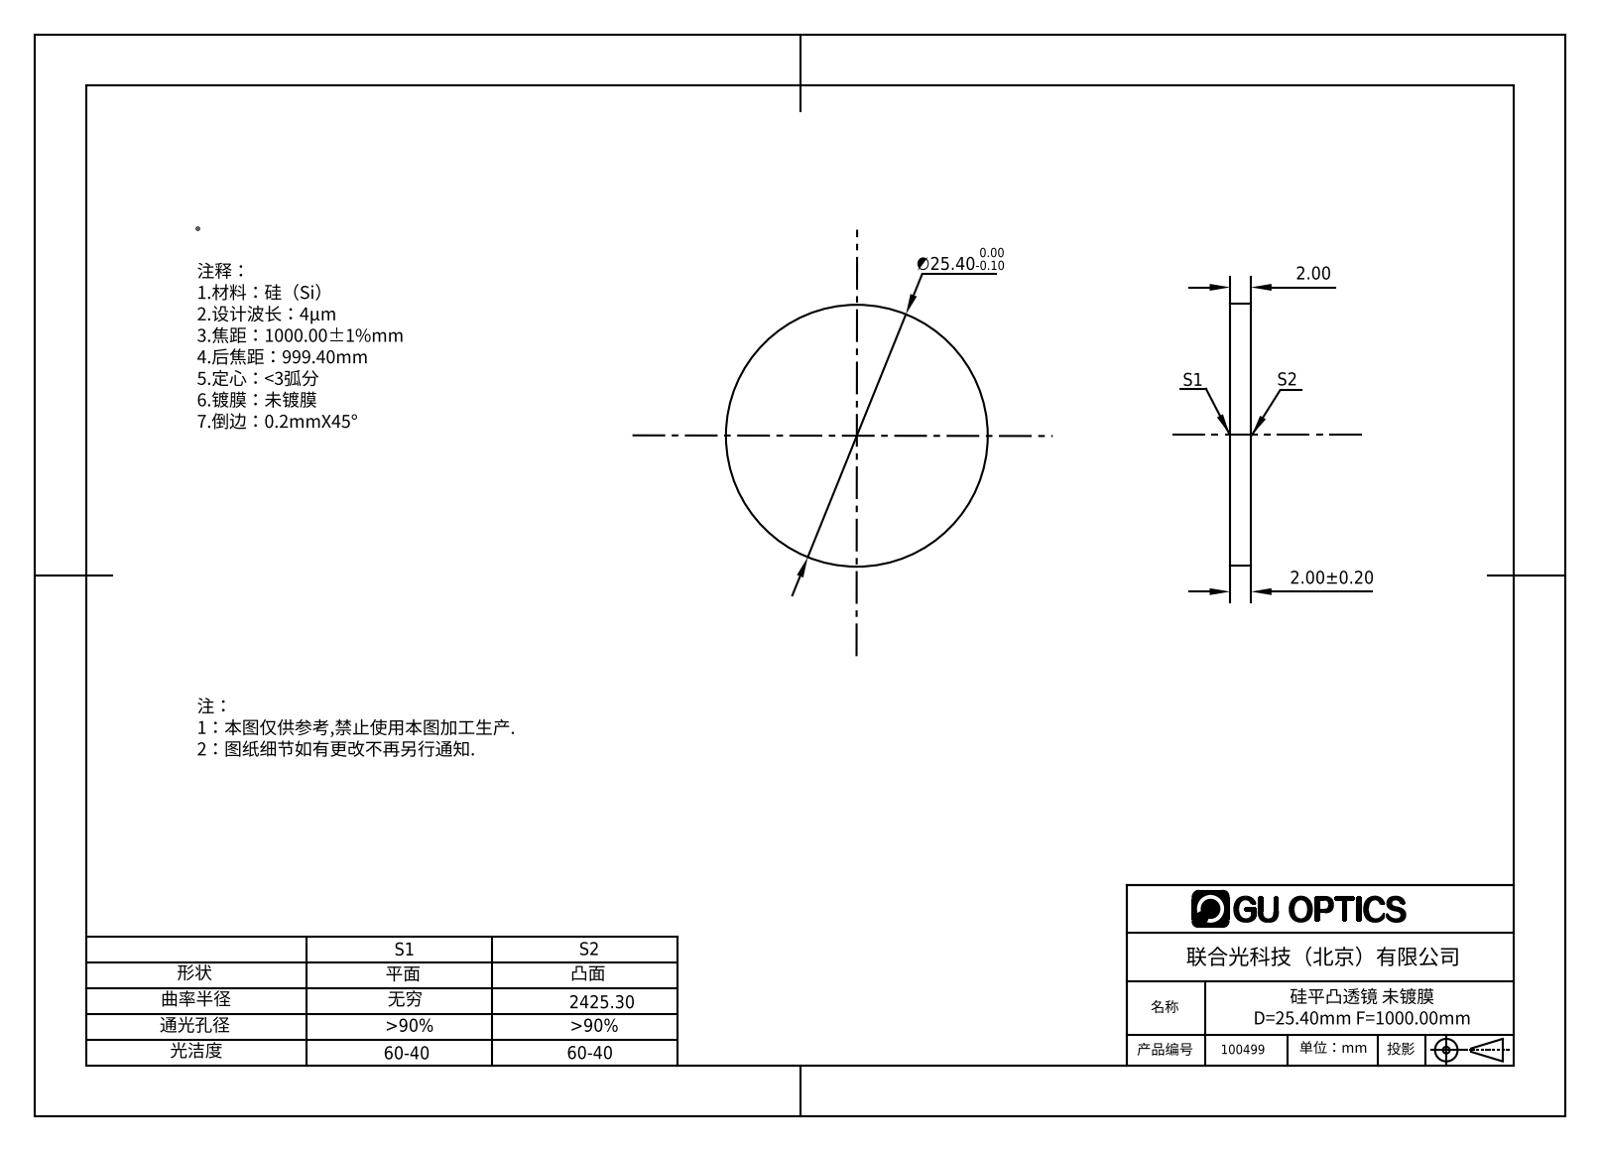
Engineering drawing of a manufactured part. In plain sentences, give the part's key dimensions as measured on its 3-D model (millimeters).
The part is named "100498". Its 3-D file was written by "SolidWorks 2016 (AUTOMOTIVE_DESIGN)". It is 1 solid with 4 faces: 2 planar, 2 cylindrical and 0 other. Overall it measures 25.4 by 25.4 by 2 millimeters. Its volume is 1 013 cubic millimeters and its surface area 1 173 square millimeters. Round bosses or shafts: 1 of diameter 25.4. The main face-to-face distances are 2.
